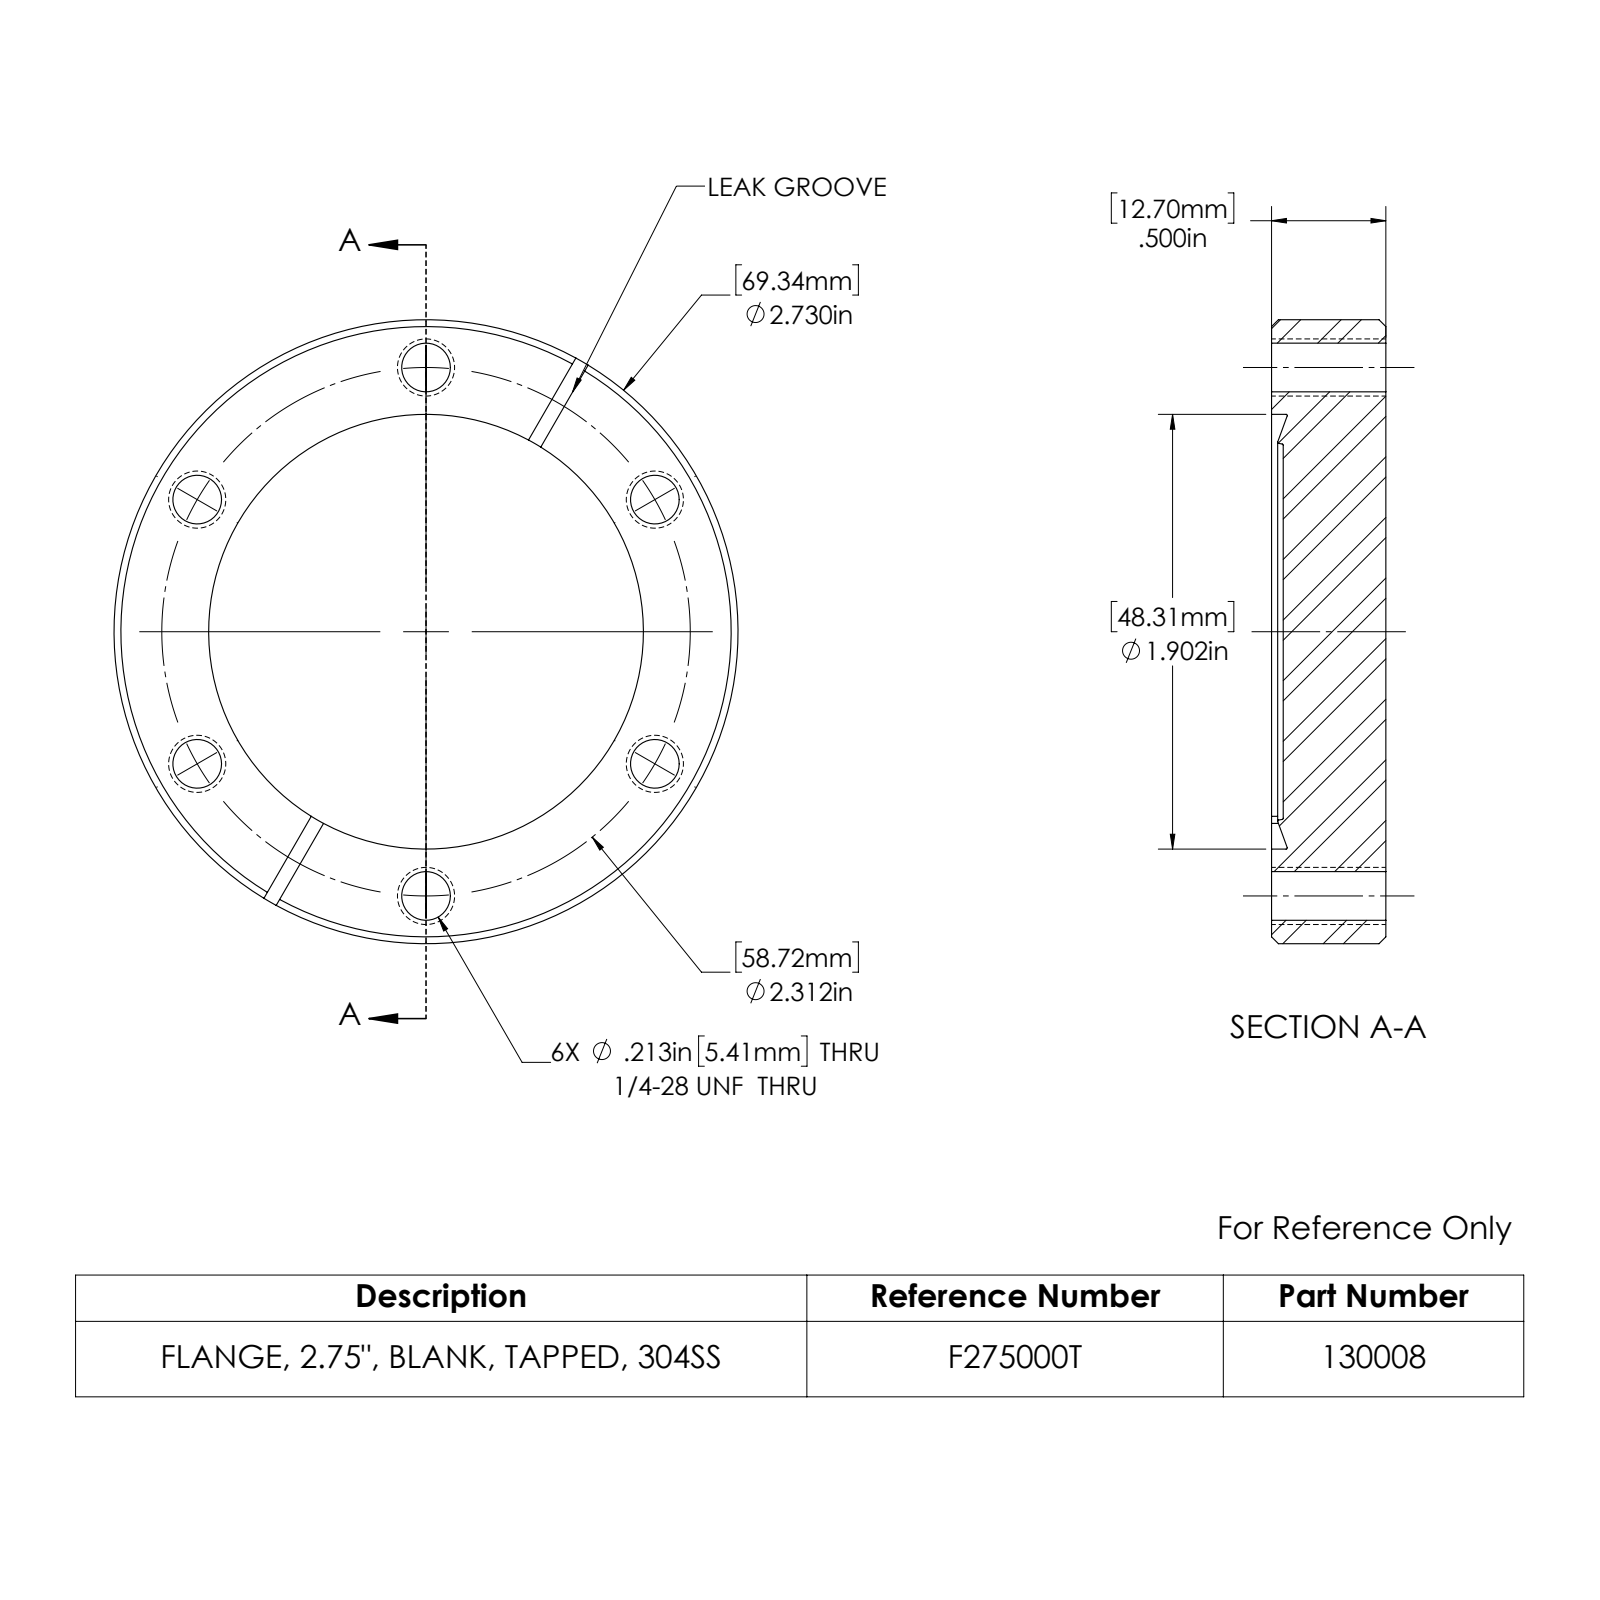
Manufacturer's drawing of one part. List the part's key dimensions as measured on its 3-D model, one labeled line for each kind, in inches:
Part name (STEP PRODUCT): 130008_D
STEP written by: SolidWorks 2022 (CONFIG_CONTROL_DESIGN)
Units: inches
Bodies: 1 solid, 41 faces (10 planar, 16 cylindrical, 15 other)
Overall size (bounding box): 2.73 × 2.73 × 0.5
Volume: 2.667 in³ · Surface area: 17.87 in²
Round holes (diameter × count): ⌀0.213 ×6, ⌀1.902 ×1
Round bosses / shafts (diameter × count): ⌀2.73 ×1
Main face-to-face distances: 0.5, 0.051, 0.449, 0.052, 0.448, 0.062
Hole centre spacings: 1.156, 2.002, 2.002, 2.312, 2.312
